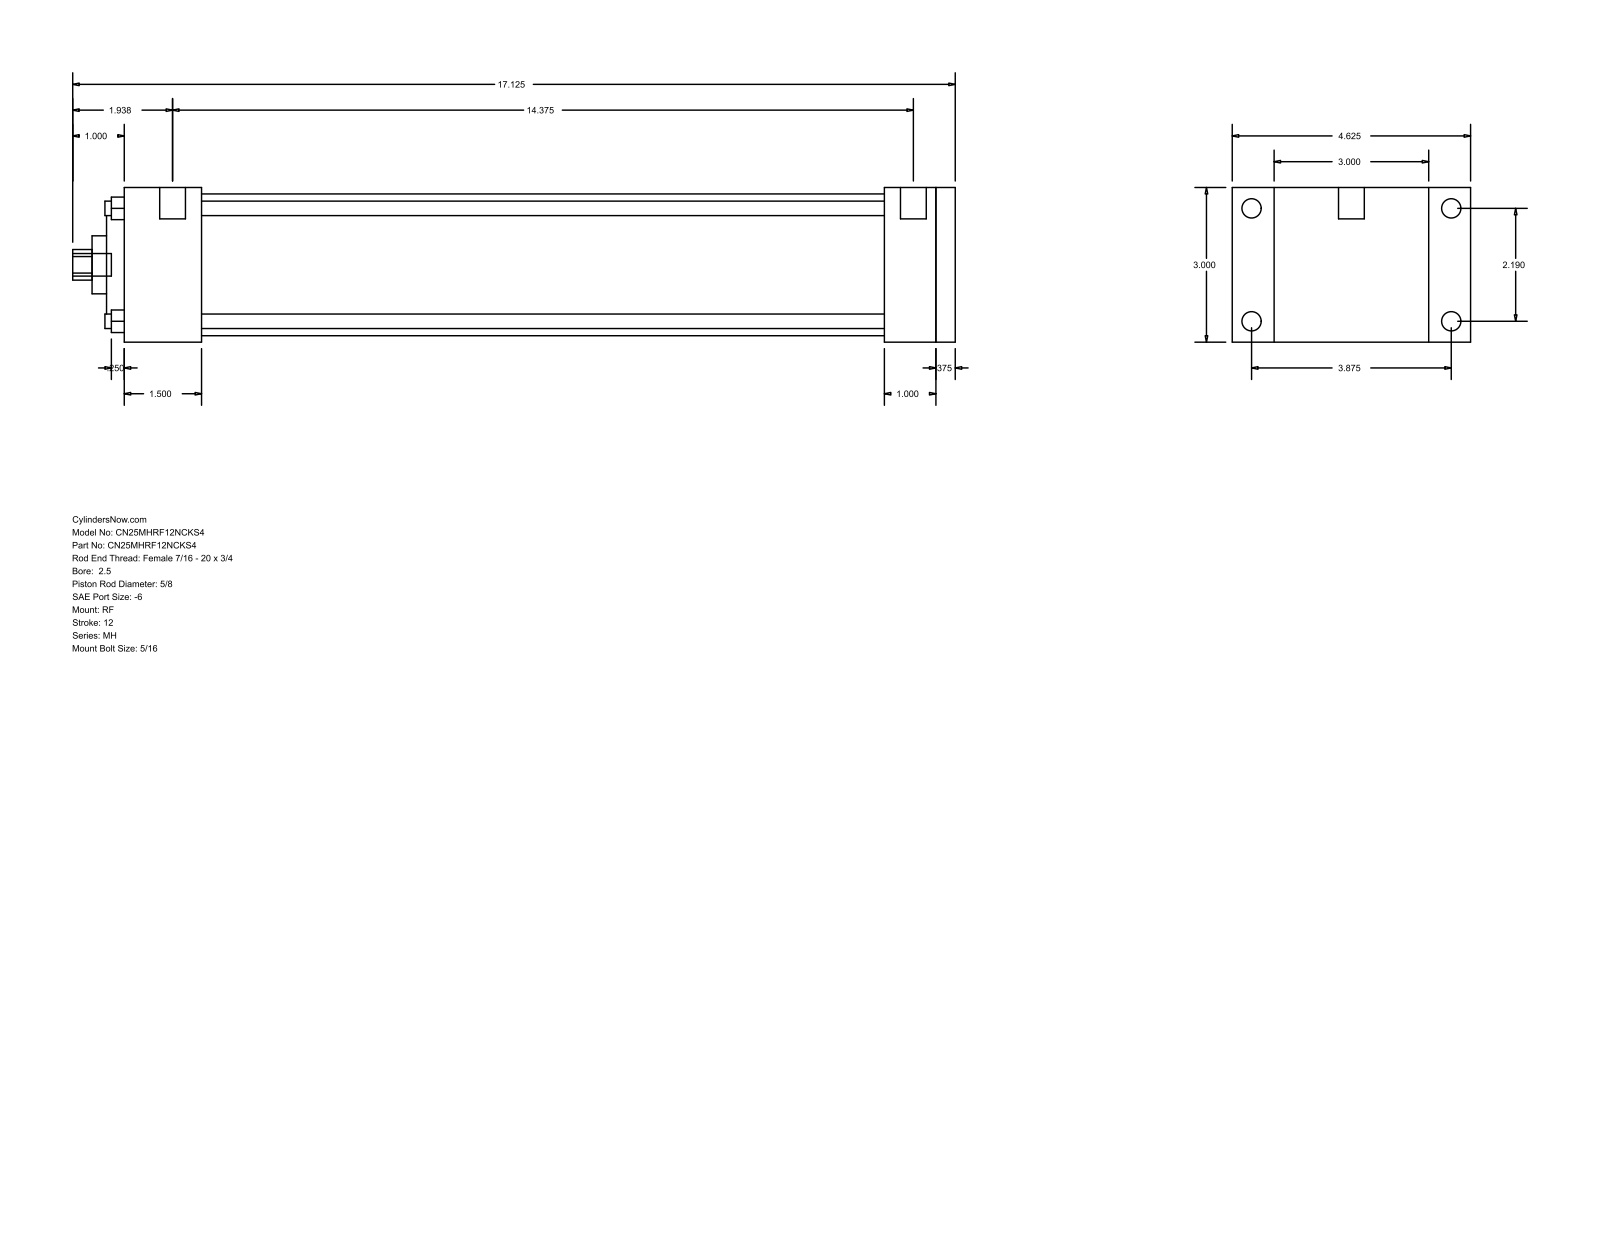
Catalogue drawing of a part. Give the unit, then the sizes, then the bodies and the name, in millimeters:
Units: millimetres
Overall size (bounding box): 434.98 × 117.47 × 76.2
Round holes (diameter × count): ⌀7.14 ×4, ⌀15.88 ×1, ⌀28.57 ×1, ⌀55.55 ×1, ⌀69.85 ×1
Round bosses / shafts (diameter × count): ⌀9.53 ×4, ⌀5.56 ×4, ⌀12.7 ×2, ⌀11.11 ×1
Partial cylindrical surfaces — rounded edges, fillets, slot ends (radius × count): R7.54 ×1
Main face-to-face distances: 76.2, 9.53, 409.58, 400.05, 25.4, 374.65, 34.93, 38.1, 336.55, 361.95
Hole centre spacings: 39.33, 55.62, 78.66
Bodies: 0 solids, 94 faces (65 planar, 29 cylindrical, 0 other)
Part name (STEP PRODUCT): MH_RF__0250_0.625
STEP written by: GSSL Pune (CONFIG_CONTROL_DESIGN)
